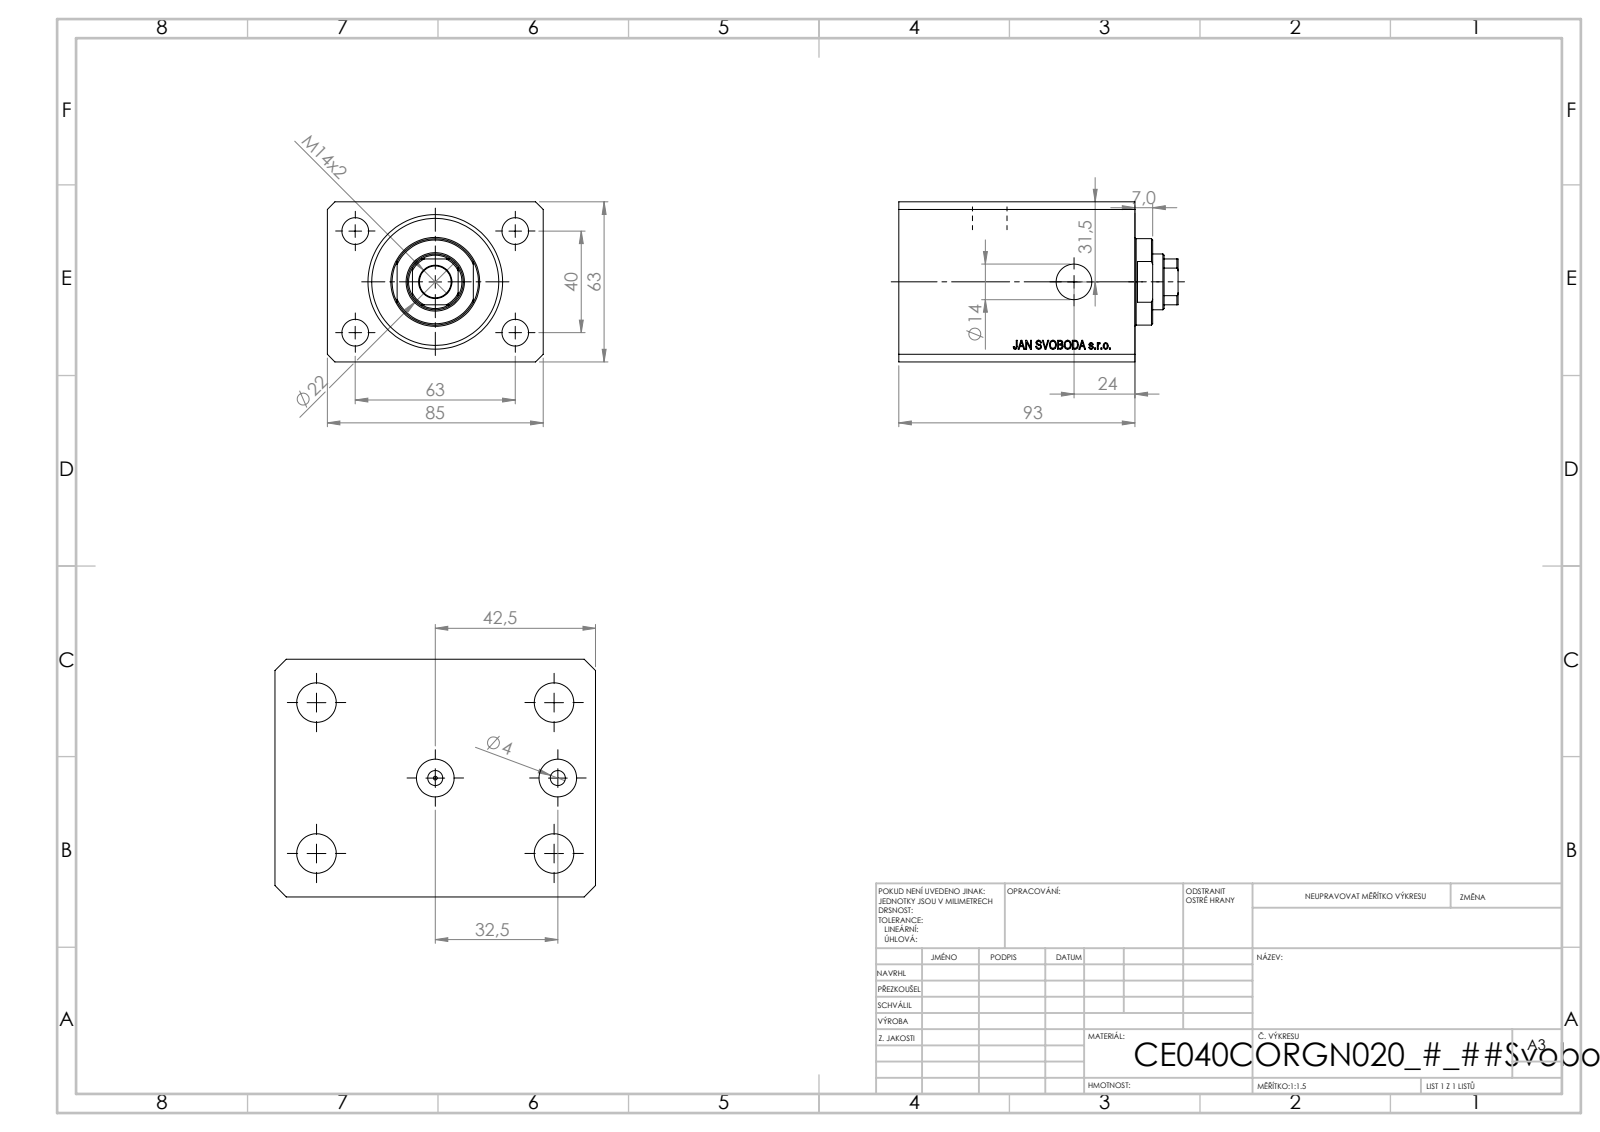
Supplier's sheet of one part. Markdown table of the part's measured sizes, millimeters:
| quantity | value |
| --- | --- |
| part name | V250CE_C_VCP; V250CE_C_Body; V250CE_VC_C |
| STEP written by | SolidWorks 2019 (CONFIG_CONTROL_DESIGN) |
| units | millimeters |
| bodies | 3 solids, 866 faces (428 planar, 44 cylindrical, 394 other) |
| overall size | 110 × 85 × 63 |
| volume | 449 801 mm³ |
| surface area | 83 942 mm² |
| round holes (diameter × count) | 10.5 × 4, 4 × 3, 10 × 2, 14 × 2, 1.25 × 1, 12.5 × 1, 22 × 1, 40 × 1, 53 × 1 |
| round bosses / shafts (diameter × count) | 34 × 1 |
| partial cylindrical surfaces (radius × count) | 10.5 × 1 |
| main face-to-face distances | 63, 85, 93, 17, 76, 11.4, 64.6, 81.6, 56, 44.6 |
| hole center spacings | 37.31, 20.02, 40, 63, 67.05, 74.63, 32.5, 45 |
